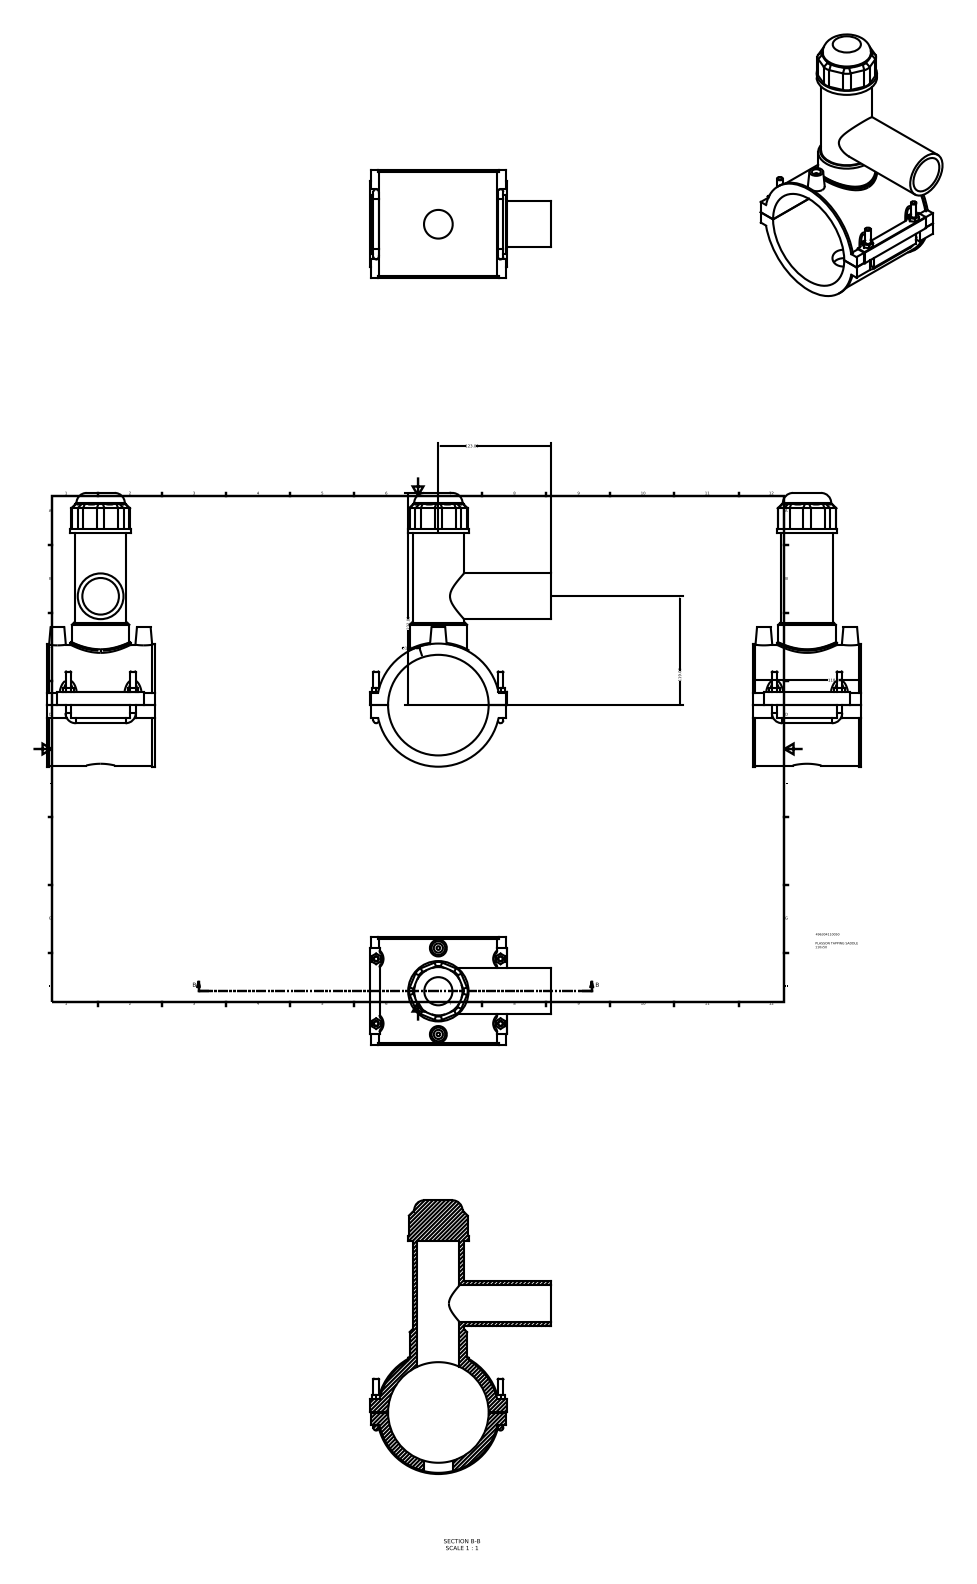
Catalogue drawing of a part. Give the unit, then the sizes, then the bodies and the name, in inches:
Units: inches
Overall size (bounding box): 11.784 × 7.795 × 4.646
Round holes (diameter × count): ⌀0.394 ×2, ⌀1.235 ×1, ⌀1.575 ×1, ⌀1.819 ×1, ⌀4.331 ×1
Round bosses / shafts (diameter × count): ⌀0.236 ×6, ⌀0.157 ×2, ⌀5.301 ×1, ⌀5.197 ×1, ⌀2.598 ×1, ⌀2.469 ×1, ⌀2.209 ×1, ⌀2.079 ×1
Partial cylindrical surfaces — rounded edges, fillets, slot ends (radius × count): R0.433 ×8, R0.118 ×4, R0.295 ×4, R0.02 ×1, R2.702 ×1
Main face-to-face distances: 4.646, 0.039, 5.866, 7.394, 7.39, 0.539, 0.543, 7.933, 0.583, 5.827
Hole centre spacings: 1.858, 3.717
Volume: 51.29 in³ · Surface area: 310.2 in²
Bodies: 1 solid, 192 faces (118 planar, 49 cylindrical, 25 other)
Part name (STEP PRODUCT): 496304110050
STEP written by: Autodesk Inventor 2015 (AUTOMOTIVE_DESIGN)
